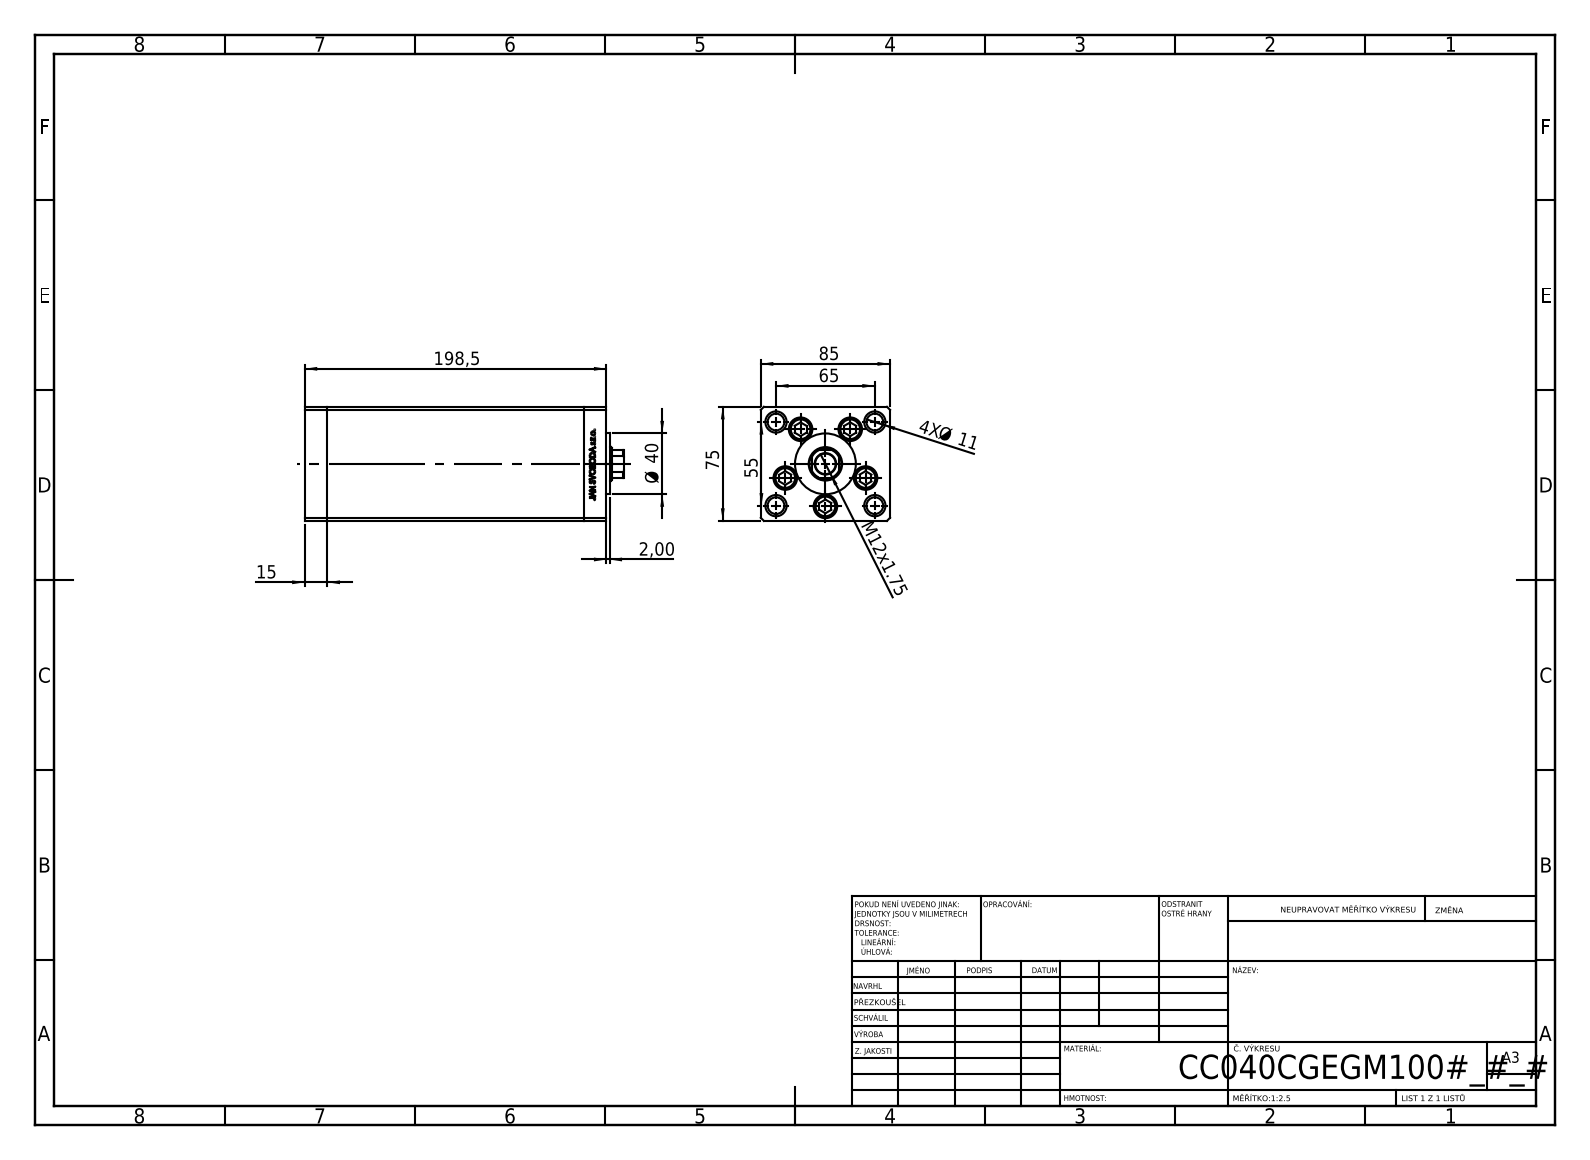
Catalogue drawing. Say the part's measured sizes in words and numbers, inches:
The part is named "V220C FRONT; V220C_C MIDDLE; ALLEN BOLT; V220C BACK_C (+1 more)". Its 3-D file was written by "SolidWorks 2019 (CONFIG_CONTROL_DESIGN)". It is 13 solids with 1163 faces: 542 planar, 159 cylindrical and 462 other. Overall it measures 8.268 by 3.346 by 2.953 inches. Its volume is 64.01 cubic inches and its surface area 298.9 square inches. Round holes: 9 of diameter 0.433, 5 of diameter 0.61, 4 of diameter 0.394, 4 of diameter 0.551, 1 of diameter 0.531, 1 of diameter 0.571, 1 of diameter 0.866. Round bosses or shafts: 5 of diameter 0.315, 4 of diameter 0.571, 1 of diameter 1.575. Partial cylindrical surfaces (rounded edges, fillets, slot ends): 2 of radius 0.037, 1 of radius 0.413. The main face-to-face distances are 3.346, 2.953, 6.634, 0.591, 7.224, 0.413, 7.815, 1.348, 2.697, 6.467. The hole center spacings are 1.102, 1.676, 0.664, 0.755, 1.273, 1.28, 1.324, 1.47.
